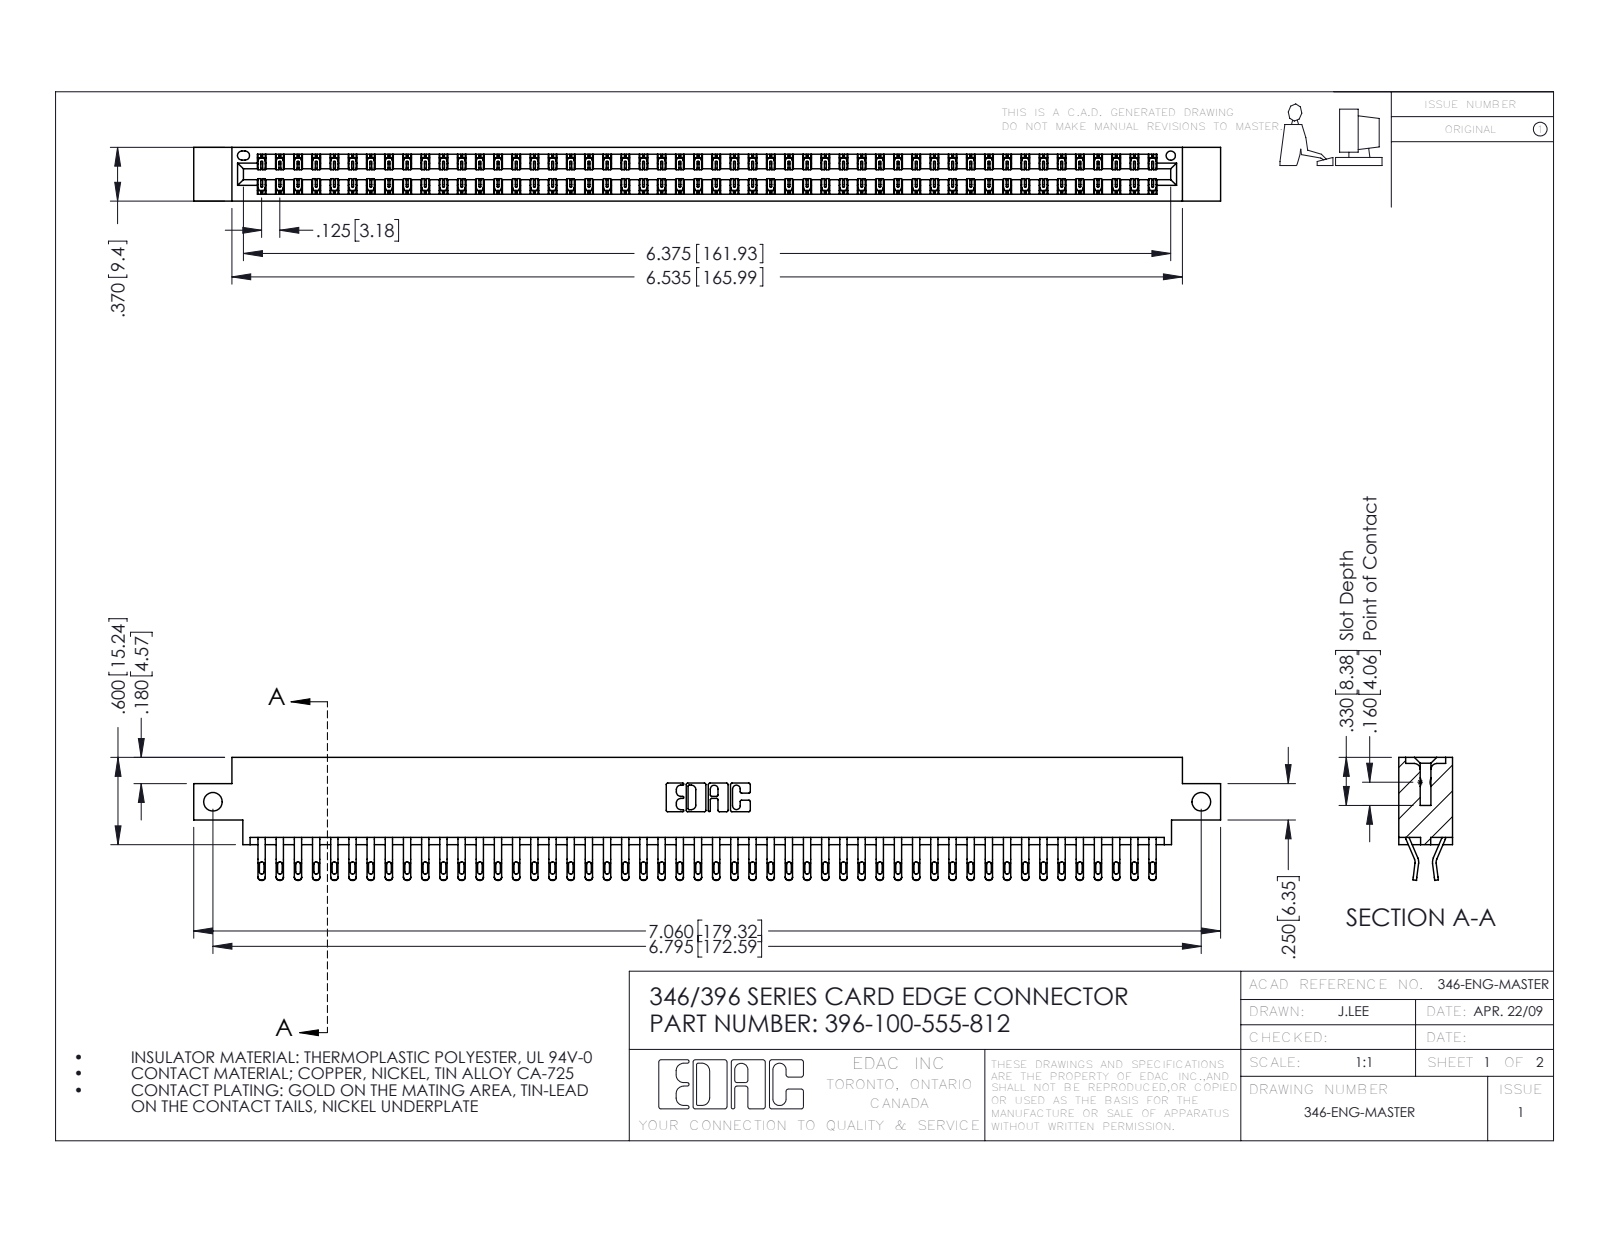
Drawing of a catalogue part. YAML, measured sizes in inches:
part_name: "396-100-555-812; 346 Part_0.170 Offset - Side Mount; 345-292-001_555 Tail"
step_written_by: "SolidWorks 2016 (CONFIG_CONTROL_DESIGN)"
units: inches
bodies: {solids: 101, faces: 5926, planar: 3380, cylindrical: 2546, other: 0}
overall_size: [7.06, 0.845, 0.37]
volume: 1.074
surface_area: 39.35
round_holes:
  - {diameter: 0.128, count: 2}
  - {diameter: 0.064, count: 1}
partial_cylinders:
  - {radius: 0.016, count: 200}
  - {radius: 0.02, count: 200}
  - {radius: 0.006, count: 150}
  - {radius: 0.01, count: 22}
  - {radius: 0.007, count: 6}
  - {radius: 0.031, count: 6}
  - {radius: 0.026, count: 3}
  - {radius: 0.01, count: 2}
face_to_face_distances: [0.048, 0.322, 0.37, 0.25, 0.025, 0.072, 0.298, 0.275, 0.148, 0.222]
hole_center_spacings: [6.795]
